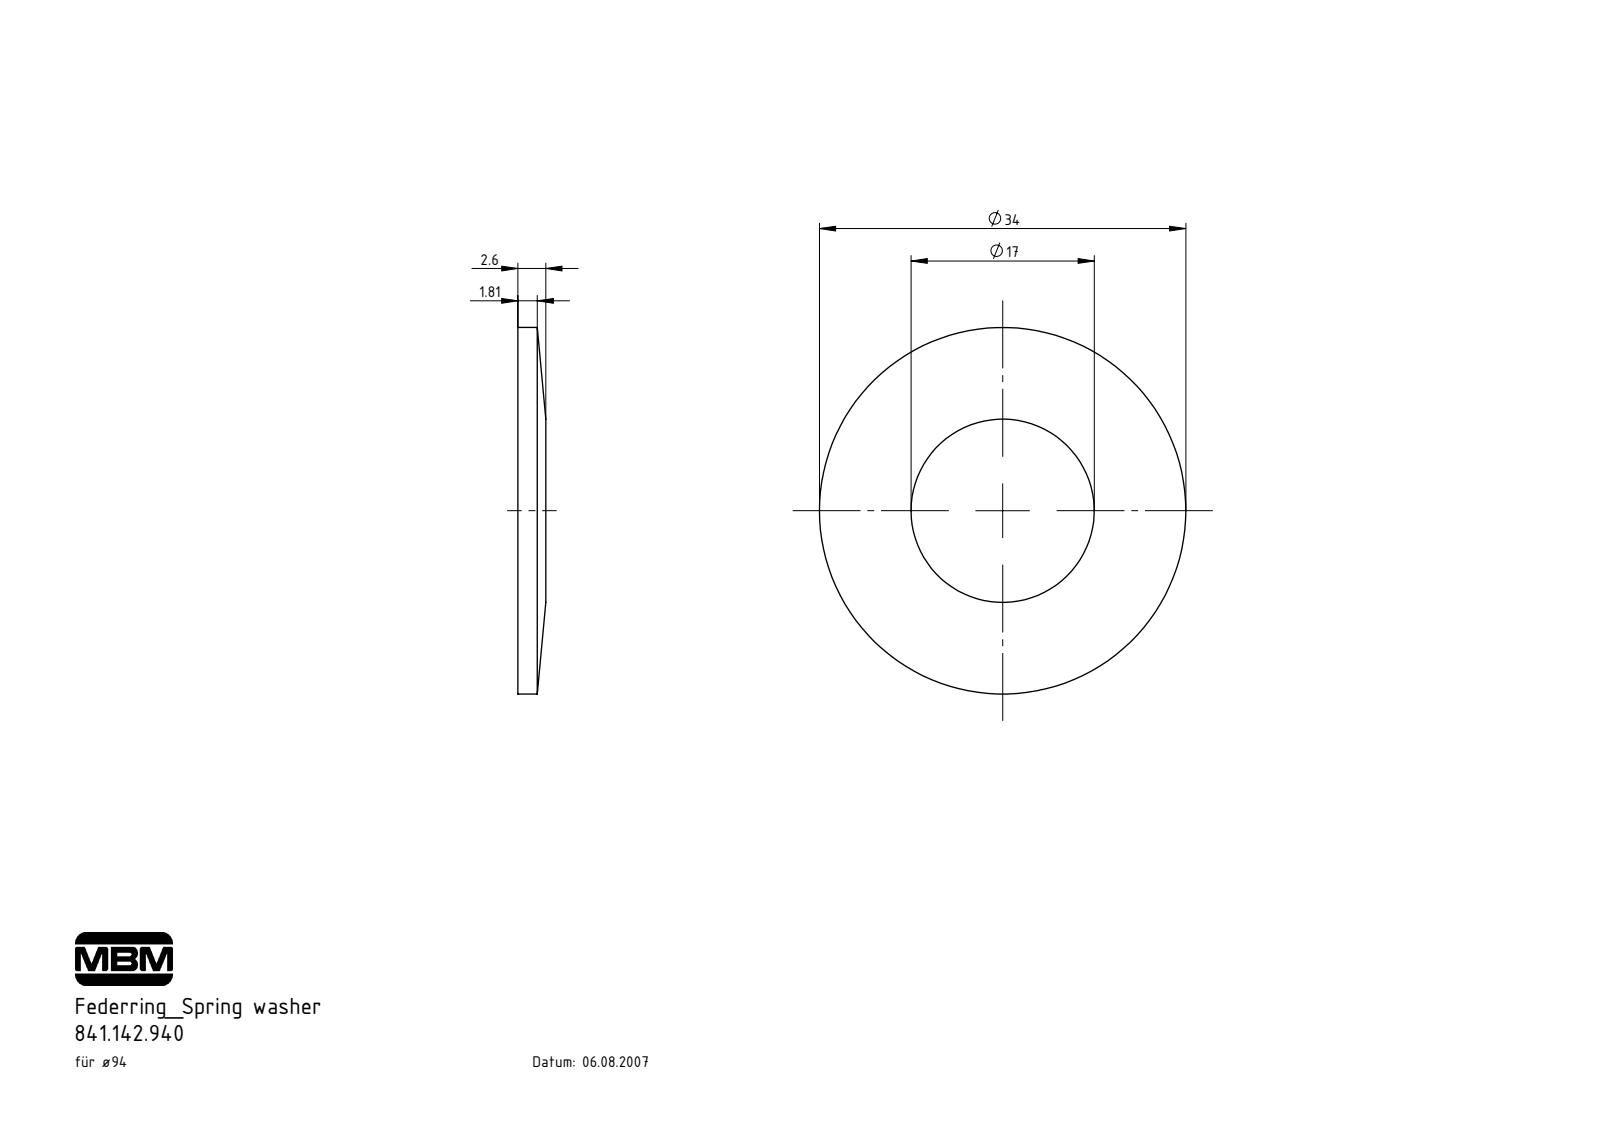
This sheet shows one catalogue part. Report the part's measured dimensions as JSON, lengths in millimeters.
{"part_name": "841.142.940", "step_written_by": "SolidWorks 2022 (AUTOMOTIVE_DESIGN)", "units": "millimeters", "bodies": {"solids": 1, "faces": 6, "planar": 2, "cylindrical": 4, "other": 0}, "overall_size": [34, 34, 1.8], "volume_mm3": 1226, "surface_area_mm2": 1650, "round_holes": [[17, 1]], "round_bosses_or_shafts": [[34, 1]], "face_to_face_distances": [1.8]}
